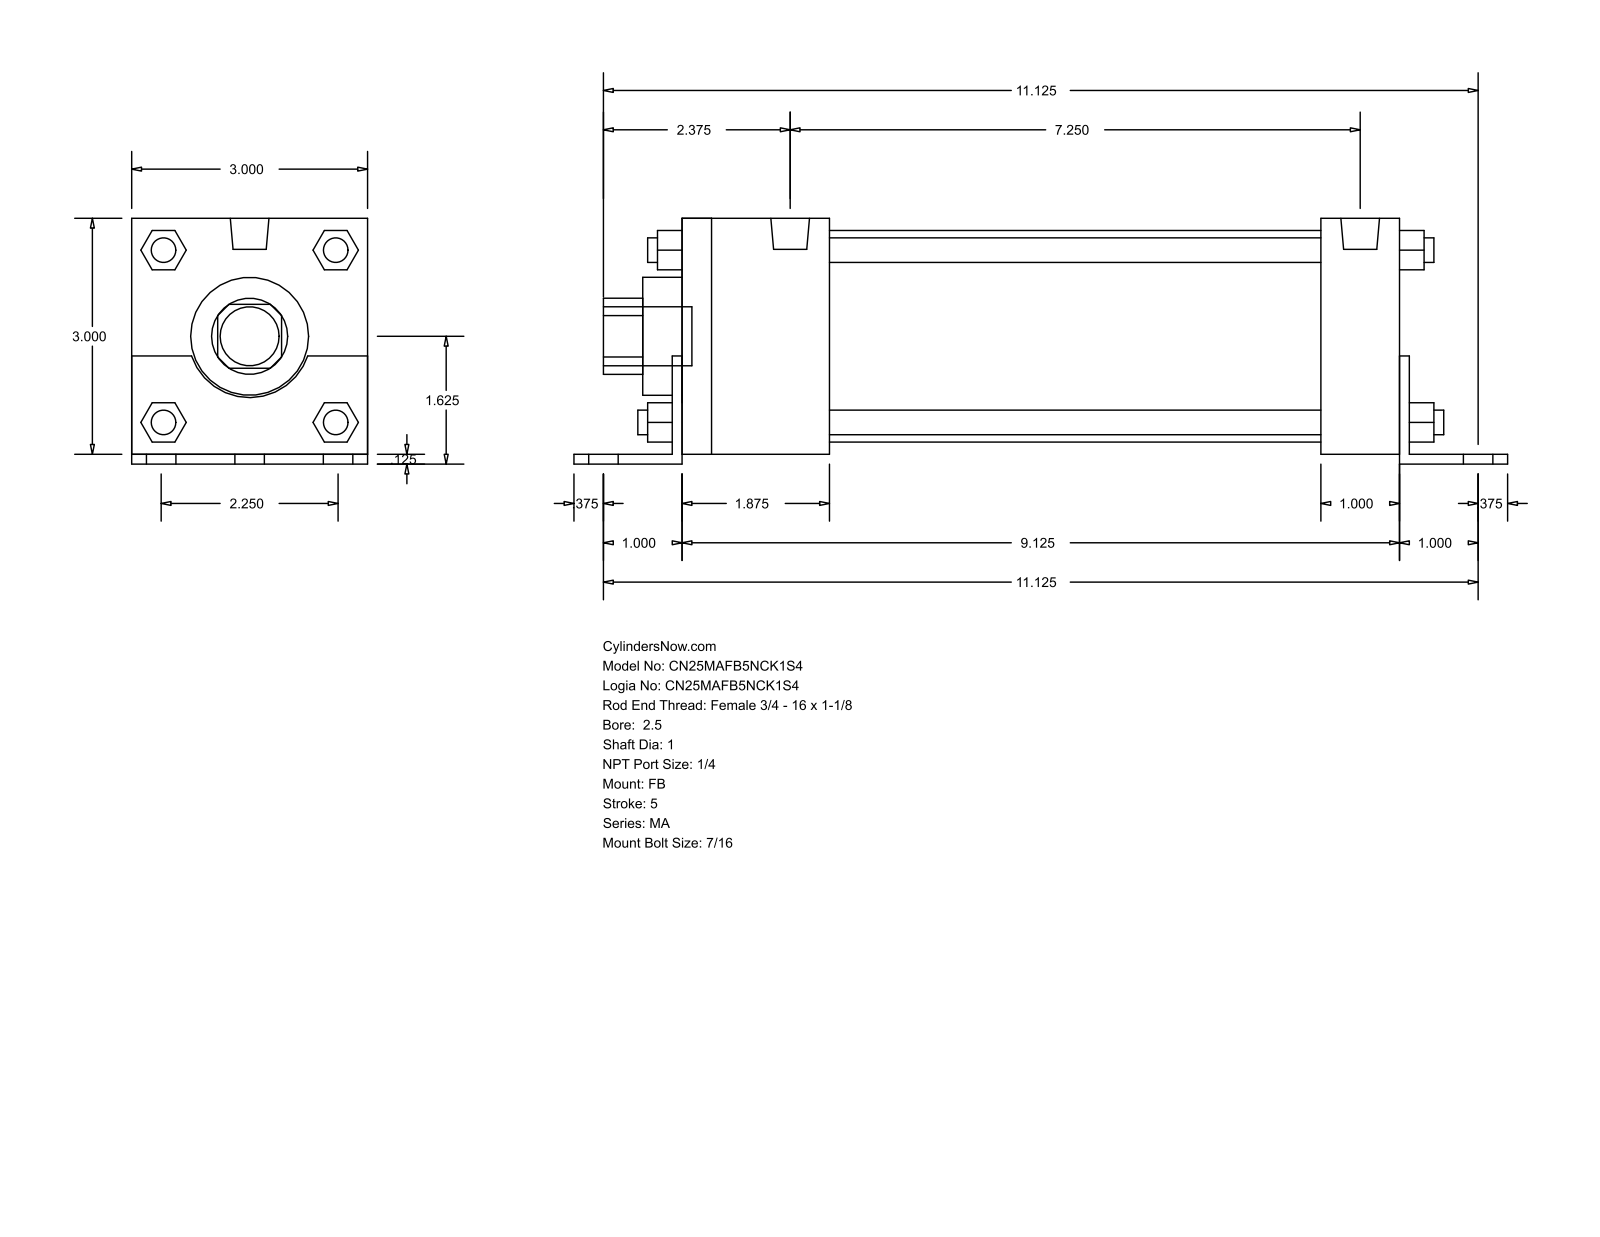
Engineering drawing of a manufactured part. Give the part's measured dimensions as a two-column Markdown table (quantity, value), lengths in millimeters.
| quantity | value |
| --- | --- |
| part name | MA_FB__0250_1 |
| STEP written by | GSSL Pune (CONFIG_CONTROL_DESIGN) |
| units | millimeters |
| bodies | 0 solids, 140 faces (105 planar, 35 cylindrical, 0 other) |
| overall size | 301.62 × 79.38 × 76.2 |
| round holes (diameter × count) | 25.4 × 1, 38.1 × 1, 68.33 × 1 |
| round bosses / shafts (diameter × count) | 7.94 × 8, 11.11 × 6, 12.49 × 2, 19.05 × 1 |
| partial cylindrical surfaces (radius × count) | 12.29 × 1, 19.81 × 1 |
| main face-to-face distances | 76.2, 3.17, 79.37, 234.95, 231.78, 12.7, 25.4, 28.57, 47.63, 184.15 |
